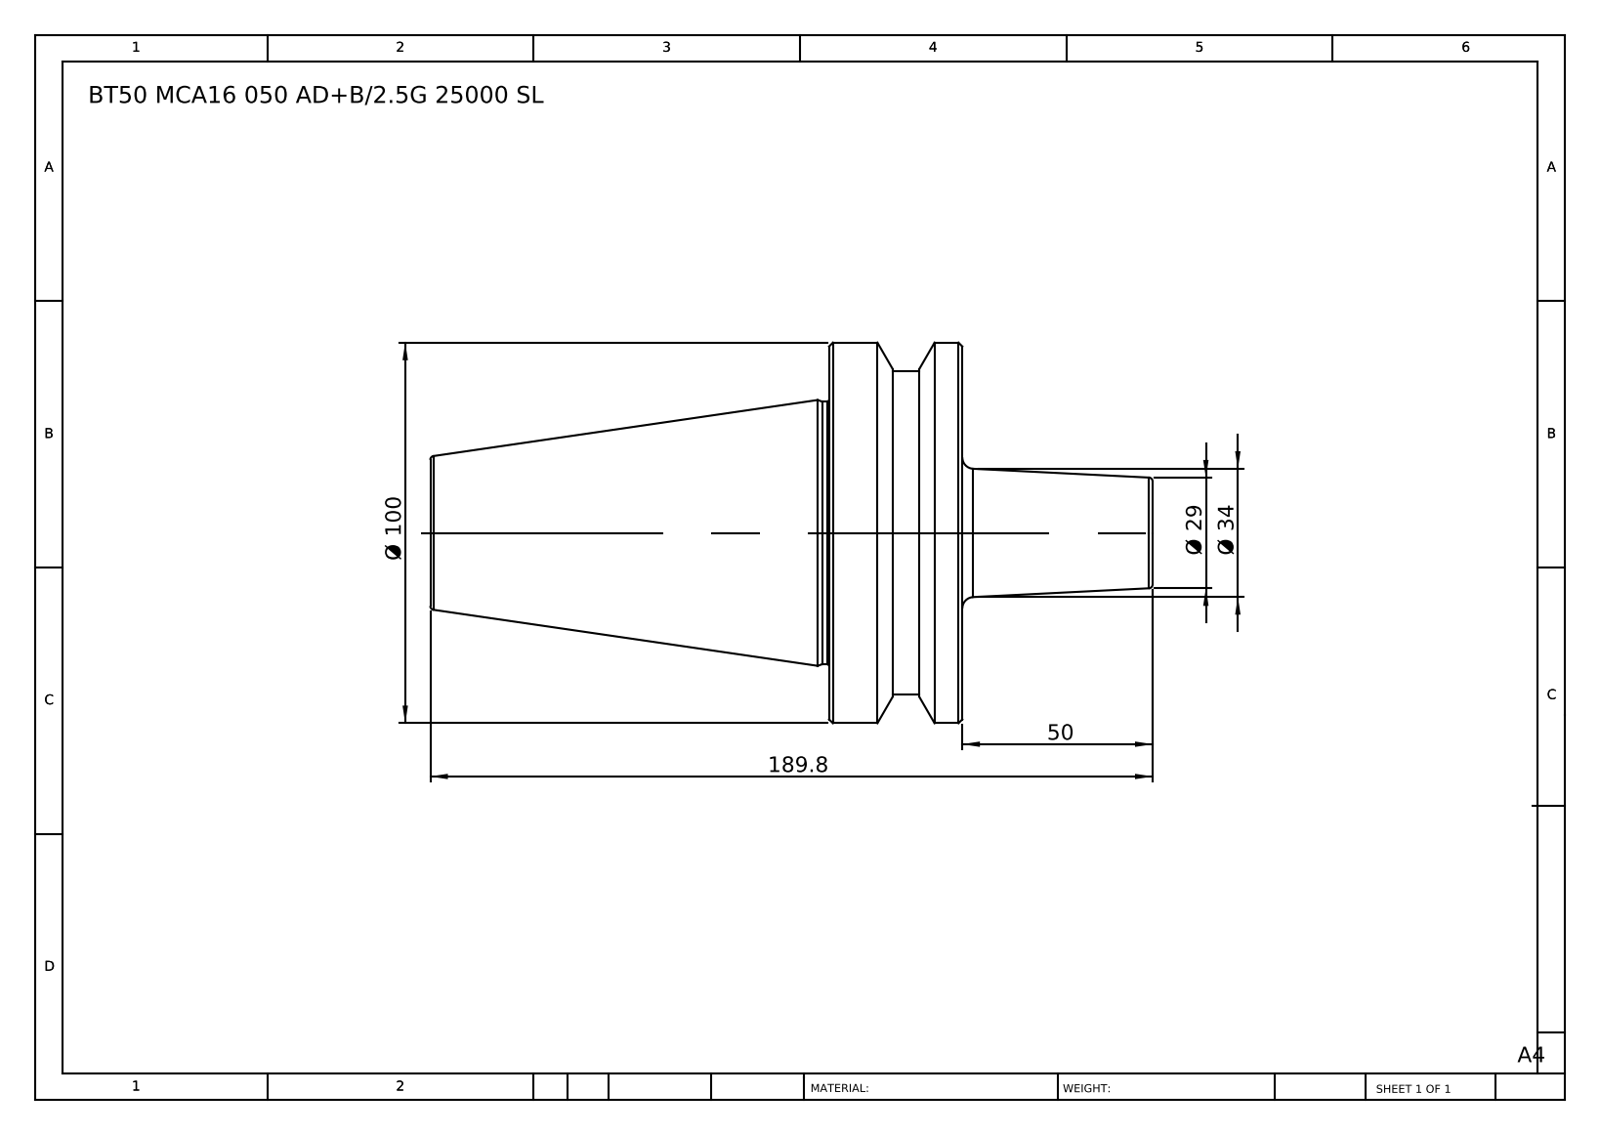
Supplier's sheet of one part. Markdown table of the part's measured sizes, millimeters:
| quantity | value |
| --- | --- |
| part name | BT50 MCA16 050 AD+B-2.5G 25000 SL |
| STEP written by | SolidWorks 2014 (CONFIG_CONTROL_DESIGN) |
| units | millimeters |
| bodies | 1 solid, 36 faces (6 planar, 8 cylindrical, 22 other) |
| overall size | 189.8 × 100 × 100 |
| volume | 549 271 mm³ |
| surface area | 48 916 mm² |
| round bosses / shafts (diameter × count) | 100 × 1, 85 × 1, 69 × 1 |
| main face-to-face distances | 35, 139.8, 104.8, 50, 85, 189.8, 61.3, 11.3, 23.7, 128.5 |
